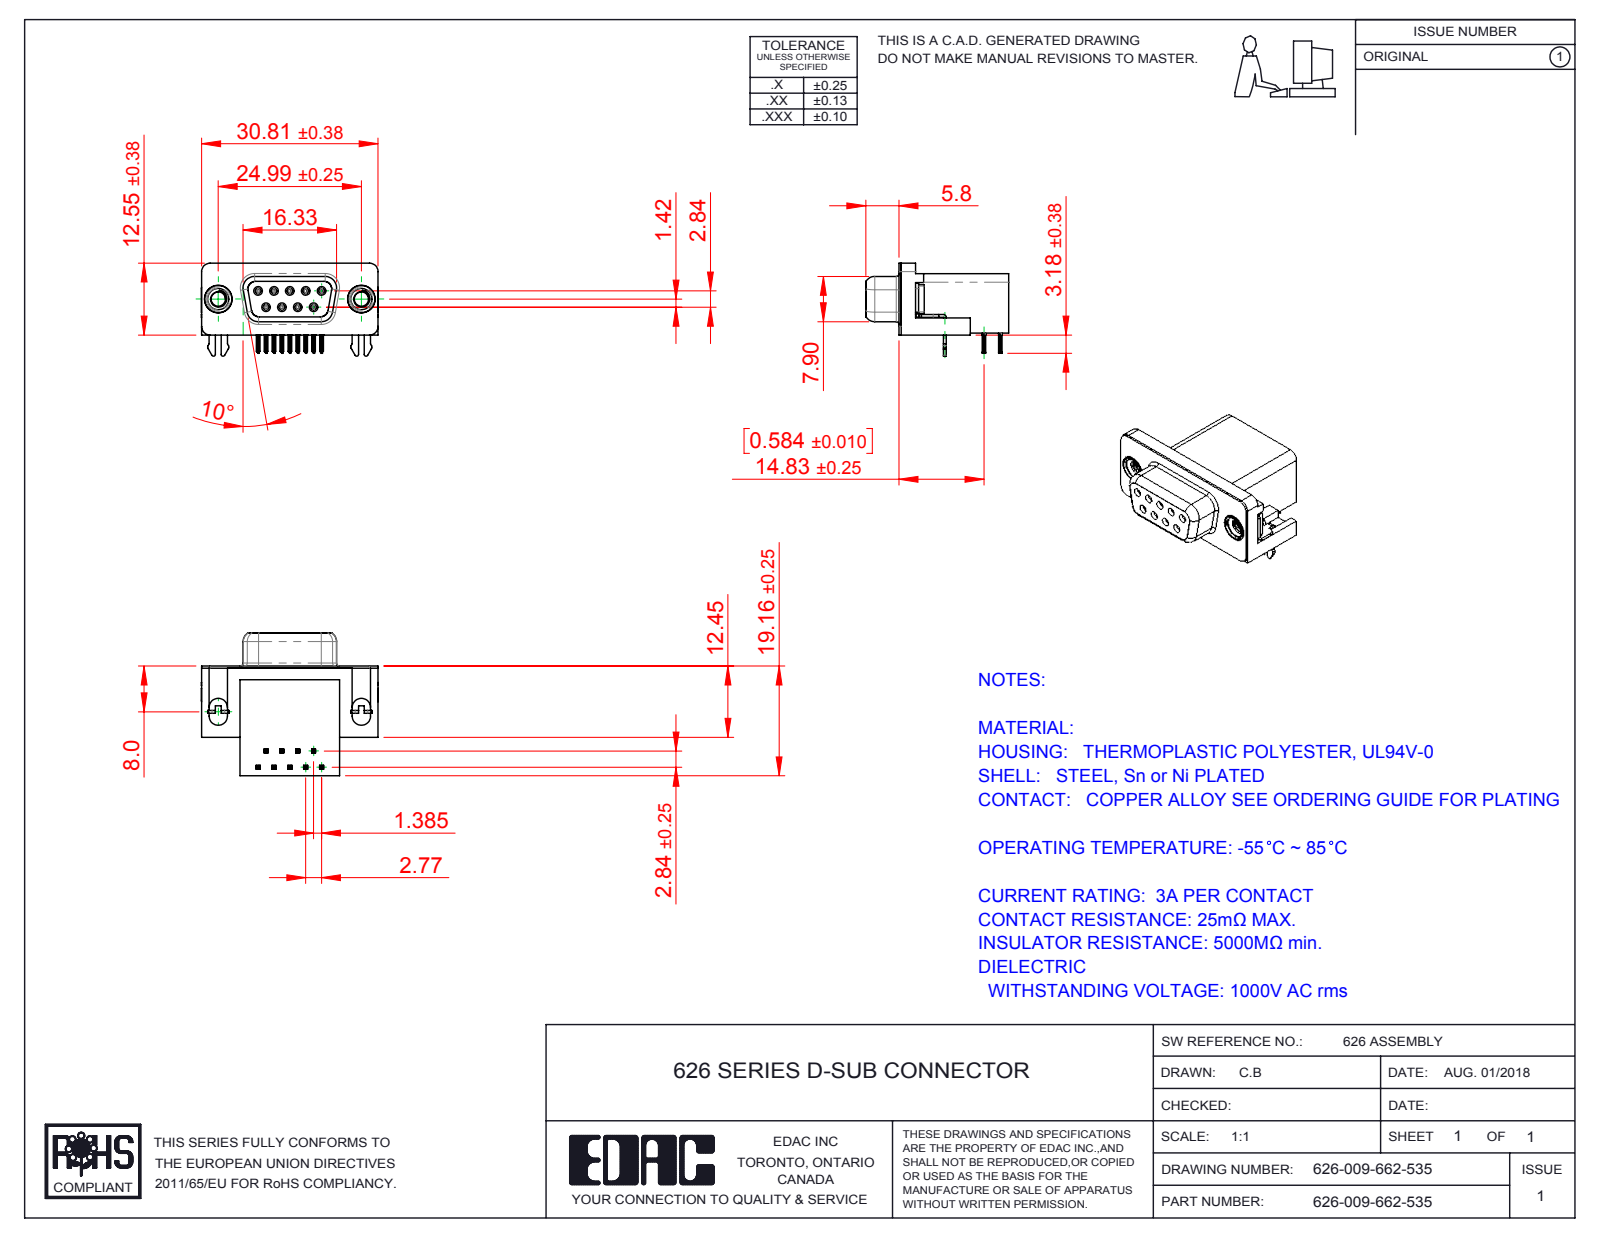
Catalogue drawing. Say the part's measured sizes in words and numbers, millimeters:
The part is named "626 Housing_9 Socket; 626 Contact Top; 626 Contact Bottom; 626 2 Prong Board Lock (+3 more)". Its 3-D file was written by "SolidWorks 2016 (CONFIG_CONTROL_DESIGN)". It is 15 solids with 1612 faces: 716 planar, 428 cylindrical and 468 other. Overall it measures 30.89 by 24.96 by 16.25 millimeters. Its volume is 4 962 cubic millimeters and its surface area 5 800 square millimeters. Round holes: 9 of diameter 0.8, 9 of diameter 0.9, 2 of diameter 2.5, 2 of diameter 4, 2 of diameter 4.8, 2 of diameter 5. Round bosses or shafts: 9 of diameter 1.2, 2 of diameter 4.9, 2 of diameter 4.75, 2 of diameter 3.9. Partial cylindrical surfaces (rounded edges, fillets, slot ends): 72 of radius 0.1, 36 of radius 0.15, 18 of radius 0.35, 18 of radius 1, 10 of radius 0.5, 9 of radius 0.34, 8 of radius 0.25, 8 of radius 1.35. The main face-to-face distances are 0.4, 10.34, 0.35, 18.76, 19.16, 2.9, 2.5, 6.2, 16.26, 0.5. The hole center spacings are 3.16, 2.77, 5.54, 5.03, 5.04, 8.31, 7.48, 7.49.
